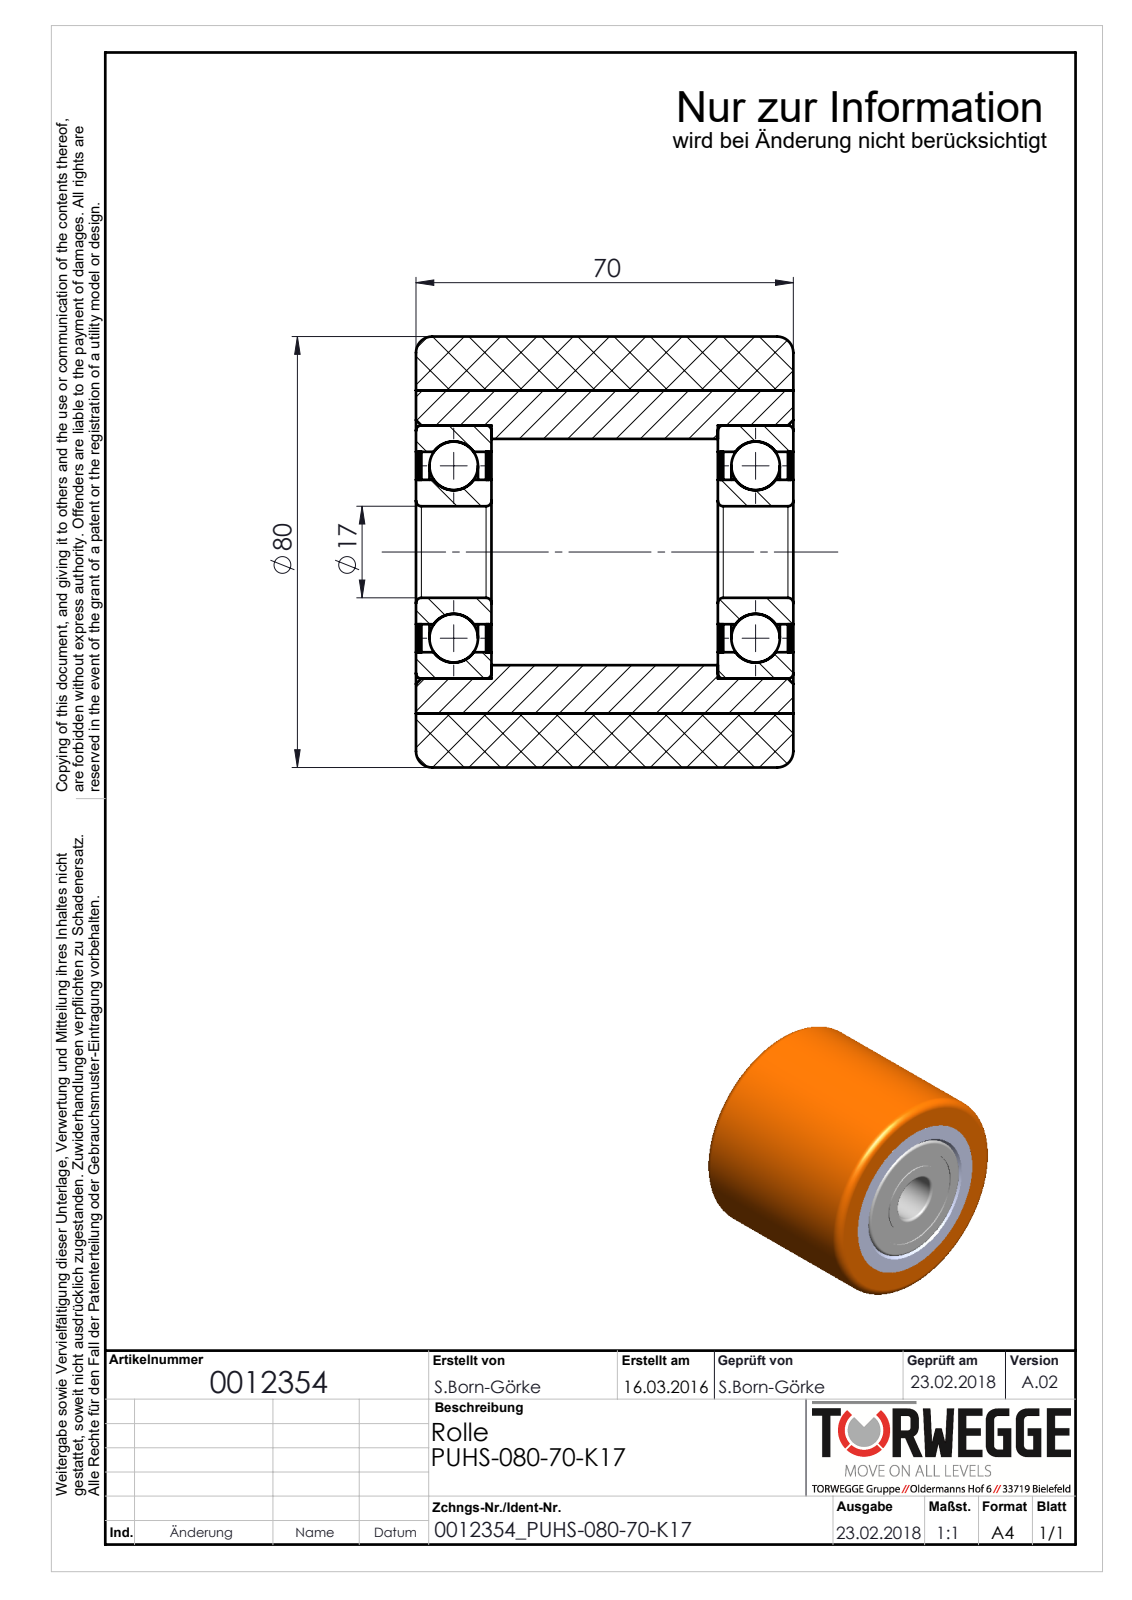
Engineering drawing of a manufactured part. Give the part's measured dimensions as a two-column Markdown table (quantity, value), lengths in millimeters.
| quantity | value |
| --- | --- |
| part name | 0012354_PUHS-080-70-K17 |
| STEP written by | SolidWorks 2016 (AUTOMOTIVE_DESIGN) |
| units | millimeters |
| bodies | 12 solids, 118 faces (22 planar, 52 cylindrical, 44 other) |
| overall size | 80 × 80 × 70 |
| volume | 280 950 mm³ |
| surface area | 85 776 mm² |
| round holes (diameter × count) | 17 × 1, 26.8 × 1, 37.2 × 1, 42 × 1, 47 × 1, 60 × 1 |
| round bosses / shafts (diameter × count) | 80 × 1 |
| main face-to-face distances | 56, 0.5, 70, 13, 14, 1, 13.5, 56.5, 12.5, 55.5 |
